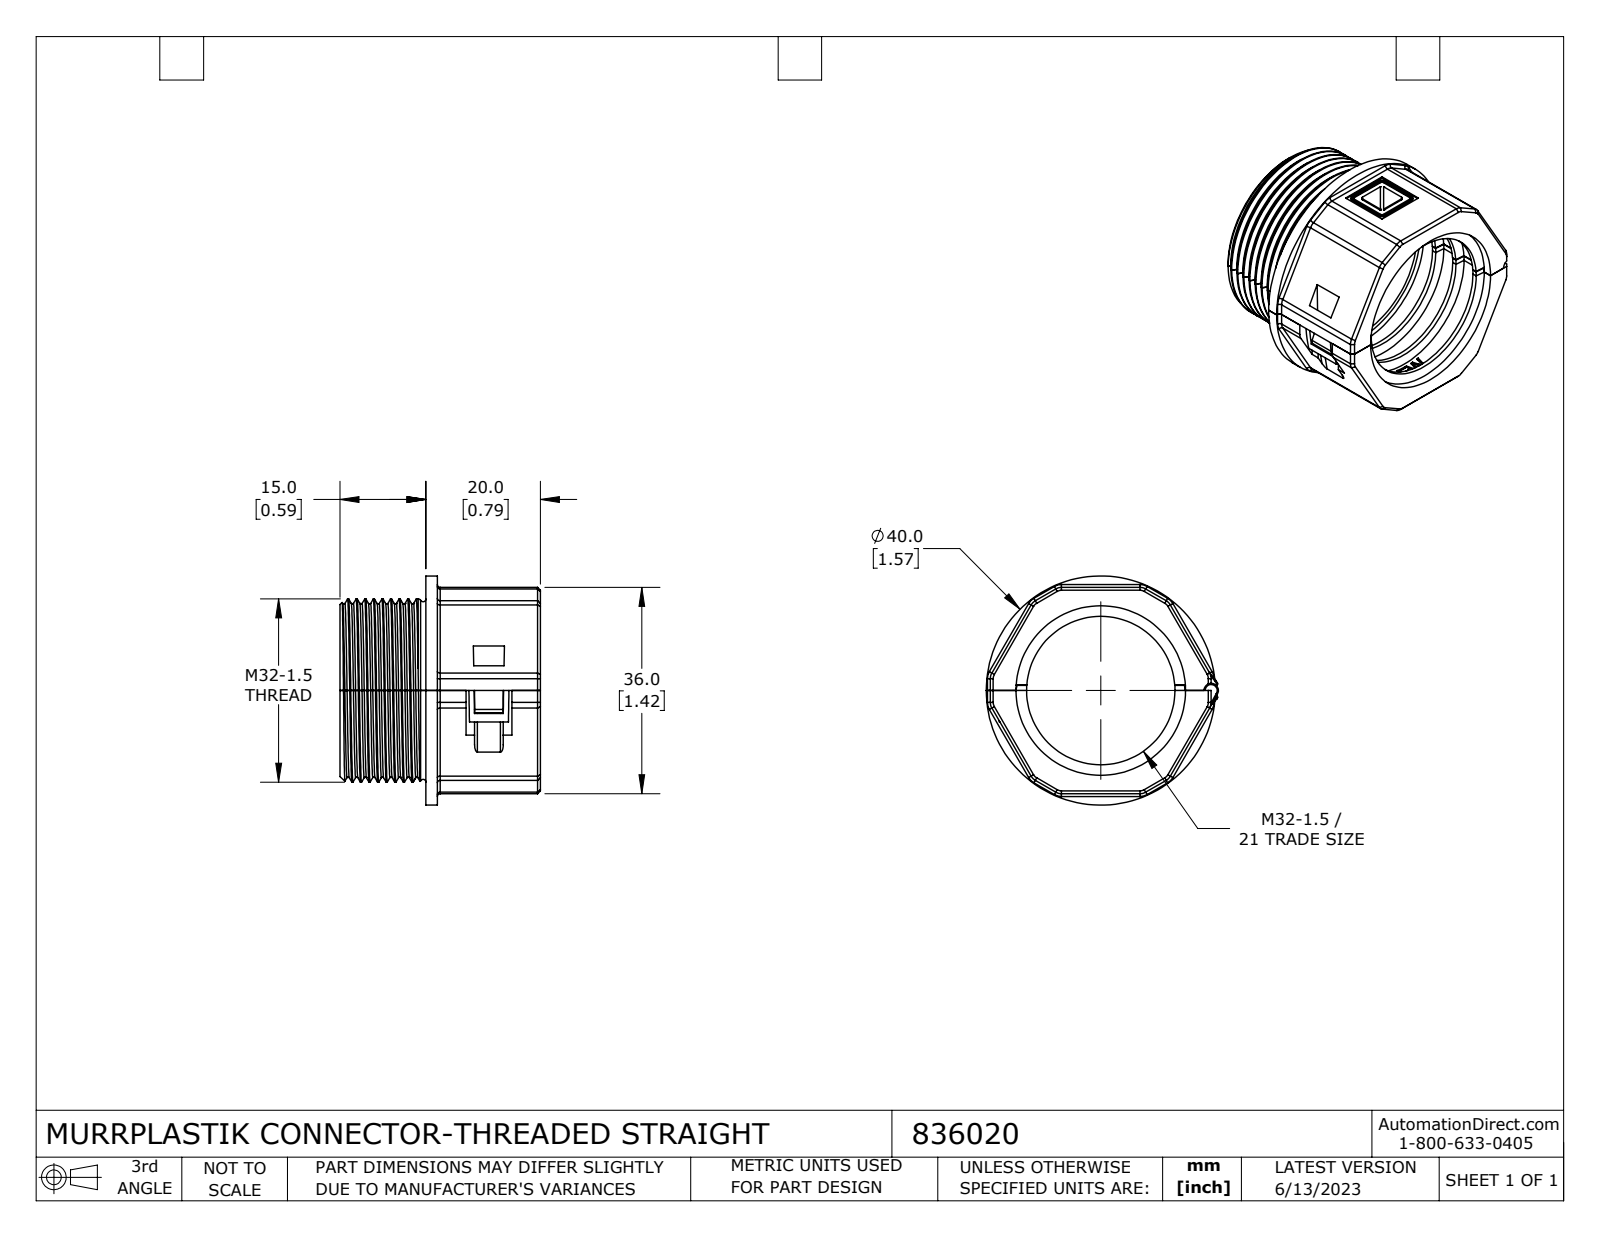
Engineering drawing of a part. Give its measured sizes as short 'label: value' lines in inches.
name: 836020
written by: SolidWorks 2021 (CONFIG_CONTROL_DESIGN)
unit: in
bodies: 2 solids, 715 faces (344 planar, 158 cylindrical, 213 other)
size: 1.596 × 1.575 × 1.378
volume: 0.727 in³; area: 17.08 in²
holes: 1× ⌀0.098, 1× ⌀0.197, 1× ⌀1.02, 1× ⌀1.063, 1× ⌀1.165
bosses: 1× ⌀1.575, 1× ⌀1.26
rounds: 27× R0.008, 22× R0.02, 13× R0.079, 4× R0.013, 4× R0.016, 4× R0.025, 4× R0.059, 1× R0.039
face distances: 0.709, 1.417, 0.787, 0.039, 0.669, 1.518, 0.591, 0.079, 0.118, 1.378
hole spacings: 0.759
